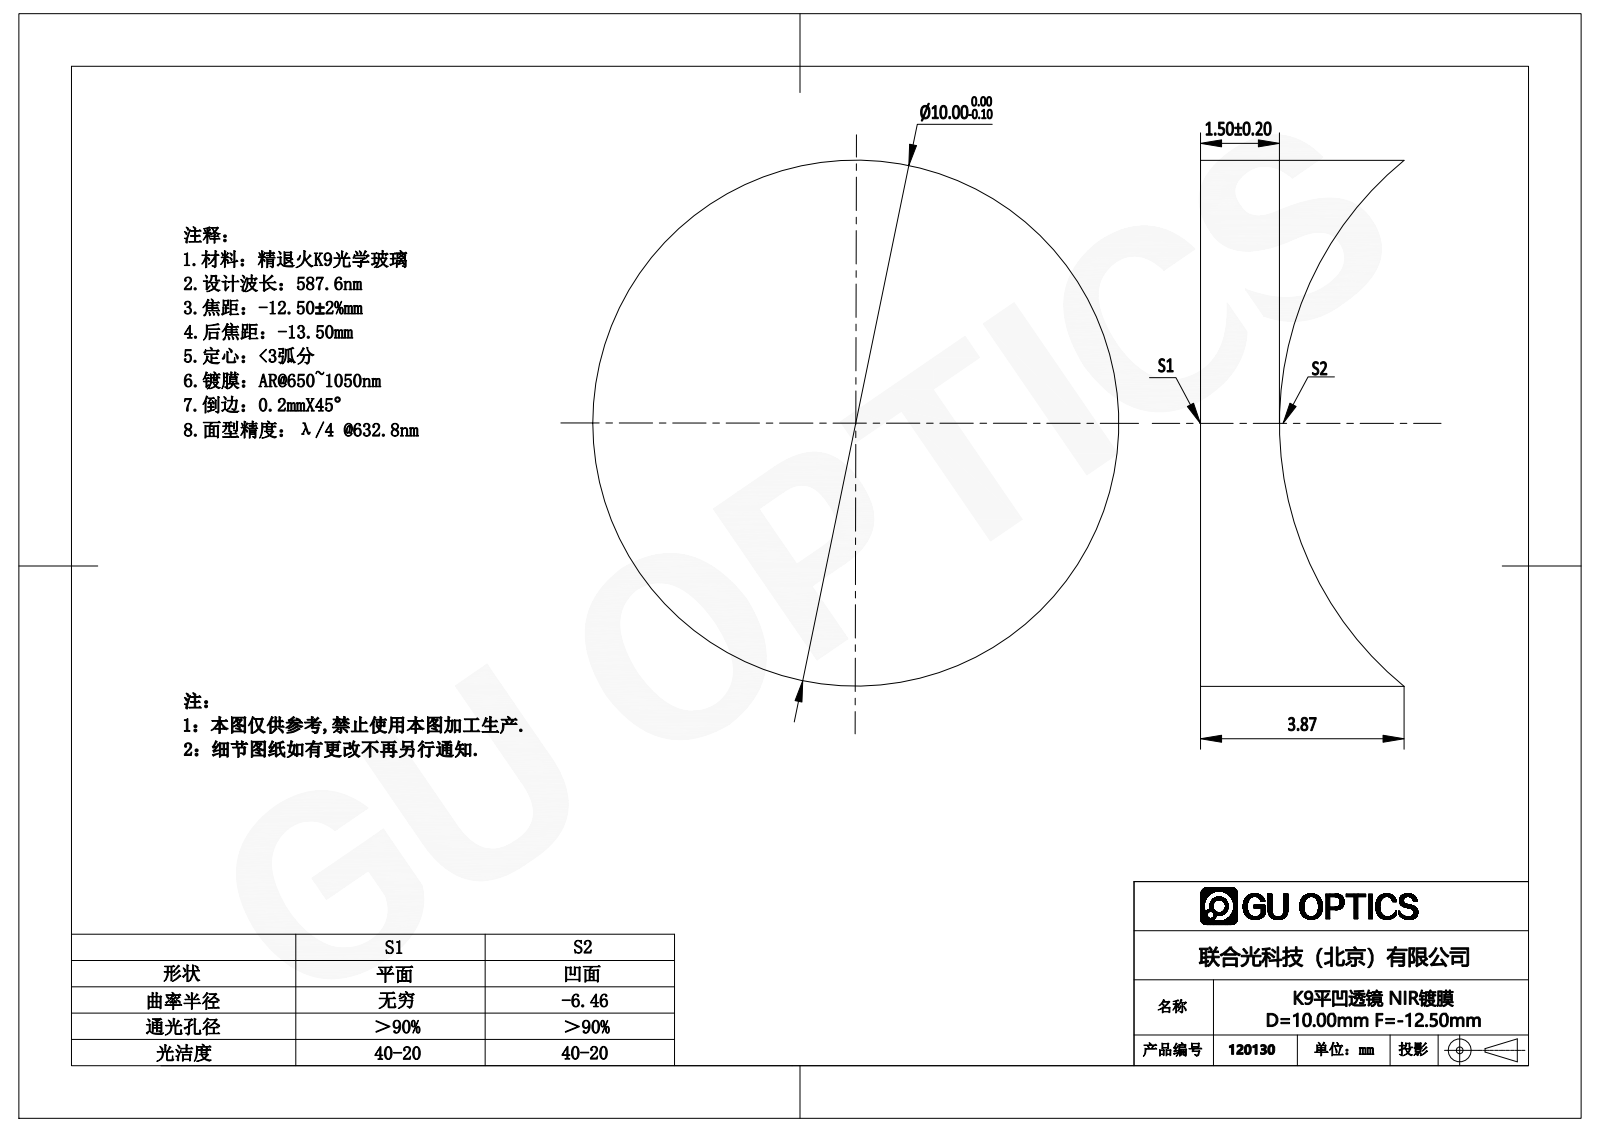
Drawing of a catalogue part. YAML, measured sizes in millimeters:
part_name: "120130"
step_written_by: "SolidWorks 2016 (AUTOMOTIVE_DESIGN)"
units: millimeters
bodies: {solids: 1, faces: 5, planar: 1, cylindrical: 2, other: 2}
overall_size: [10, 10, 3.87]
volume: 204
surface_area: 296
round_bosses_or_shafts:
  - {diameter: 10, count: 1}
